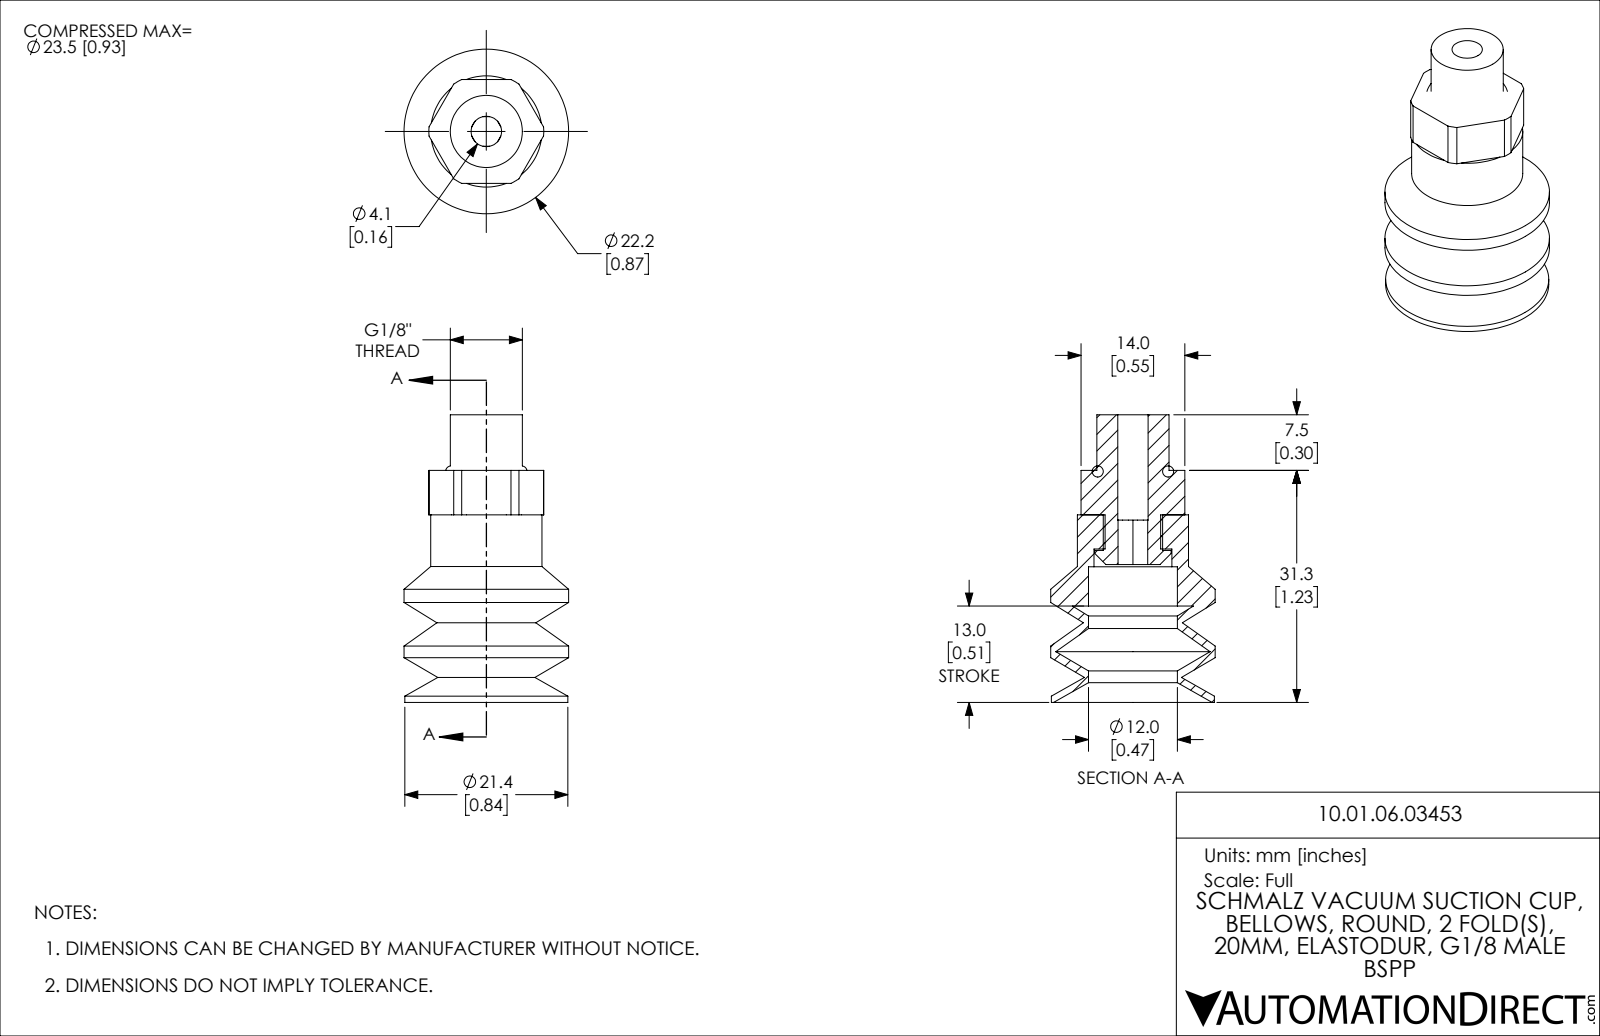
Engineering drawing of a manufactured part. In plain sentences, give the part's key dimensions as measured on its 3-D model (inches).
The part is named "10.01.06.03453". Its 3-D file was written by "SolidWorks 2021 (CONFIG_CONTROL_DESIGN)". It is 3 solids with 91 faces: 34 planar, 33 cylindrical and 24 other. Overall it measures 1.528 by 0.874 by 0.874 inches. Its volume is 0.291 cubic inches and its surface area 8.187 square inches. Round holes: 1 of diameter 0.161, 1 of diameter 0.295, 1 of diameter 0.413, 1 of diameter 0.472. Round bosses or shafts: 1 of diameter 0.874, 1 of diameter 0.866, 1 of diameter 0.591, 1 of diameter 0.406, 1 of diameter 0.383, 1 of diameter 0.315. Partial cylindrical surfaces (rounded edges, fillets, slot ends): 1 of radius 0.305. The main face-to-face distances are 0.72, 0.551, 0.484, 0.236, 0.295, 0.197, 0.354, 1.016, 0.531, 0.512.
